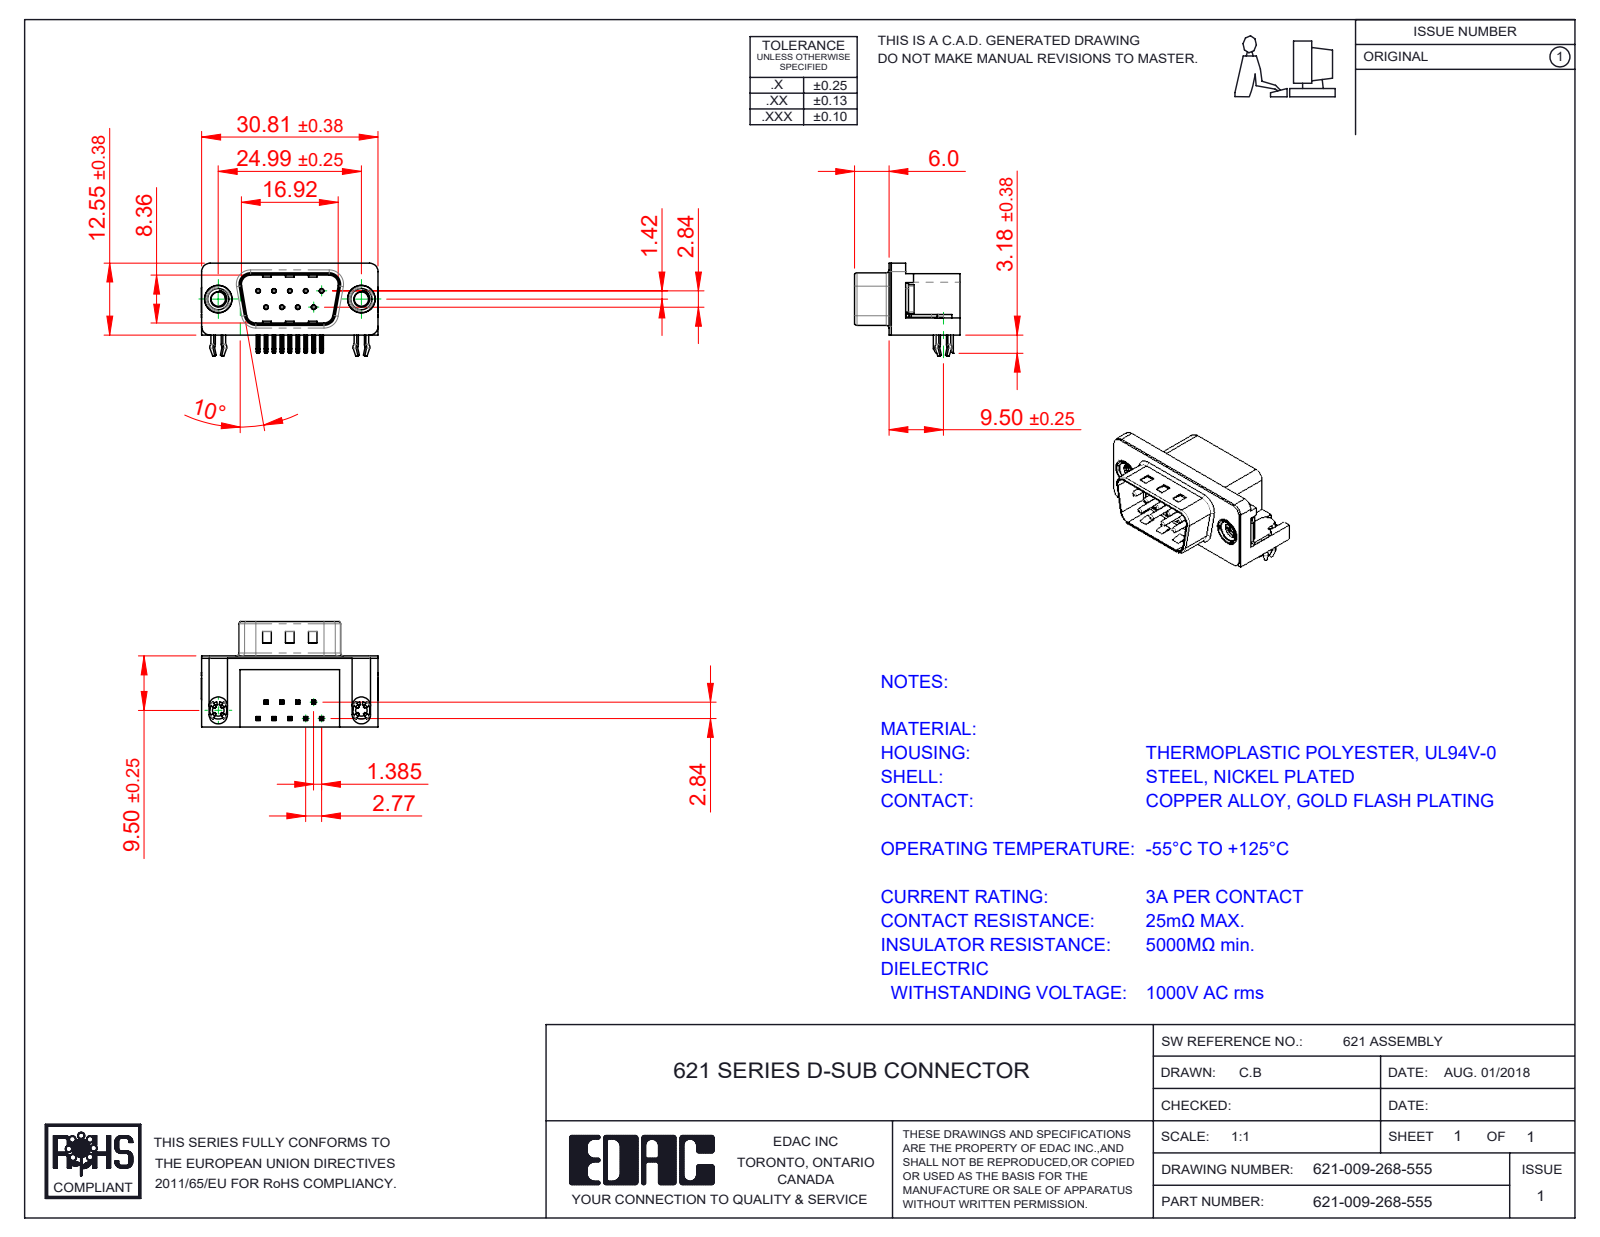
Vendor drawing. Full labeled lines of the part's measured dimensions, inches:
Part name (STEP PRODUCT): 621 4-40 Threaded Board Mount; 621-009-268-555; 621 Shell_9 Socket; 621 M3 Threaded Rivet (+3 more)
STEP written by: SolidWorks 2016 (CONFIG_CONTROL_DESIGN)
Units: inches
Bodies: 15 solids, 1021 faces (573 planar, 331 cylindrical, 117 other)
Overall size (bounding box): 1.216 × 0.724 × 0.619
Volume: 0.198 in³ · Surface area: 6.98 in²
Round holes (diameter × count): ⌀0.014 ×9, ⌀0.031 ×9, ⌀0.089 ×2, ⌀0.098 ×2, ⌀0.157 ×2, ⌀0.189 ×2, ⌀0.197 ×2
Round bosses / shafts (diameter × count): ⌀0.03 ×9, ⌀0.193 ×2, ⌀0.187 ×2, ⌀0.154 ×2, ⌀0.128 ×2
Partial cylindrical surfaces — rounded edges, fillets, slot ends (radius × count): R0.01 ×44, R0.005 ×18, R0.039 ×16, R0.02 ×9, R0.059 ×8, R0.063 ×8, R0.035 ×4, R0.079 ×4
Main face-to-face distances: 0.016, 0.472, 0.488, 0.407, 0.114, 0.374, 0.098, 0.02, 0.083, 0.014
Hole centre spacings: 0.124, 0.109, 0.218, 0.198, 0.198, 0.327, 0.294, 0.295
